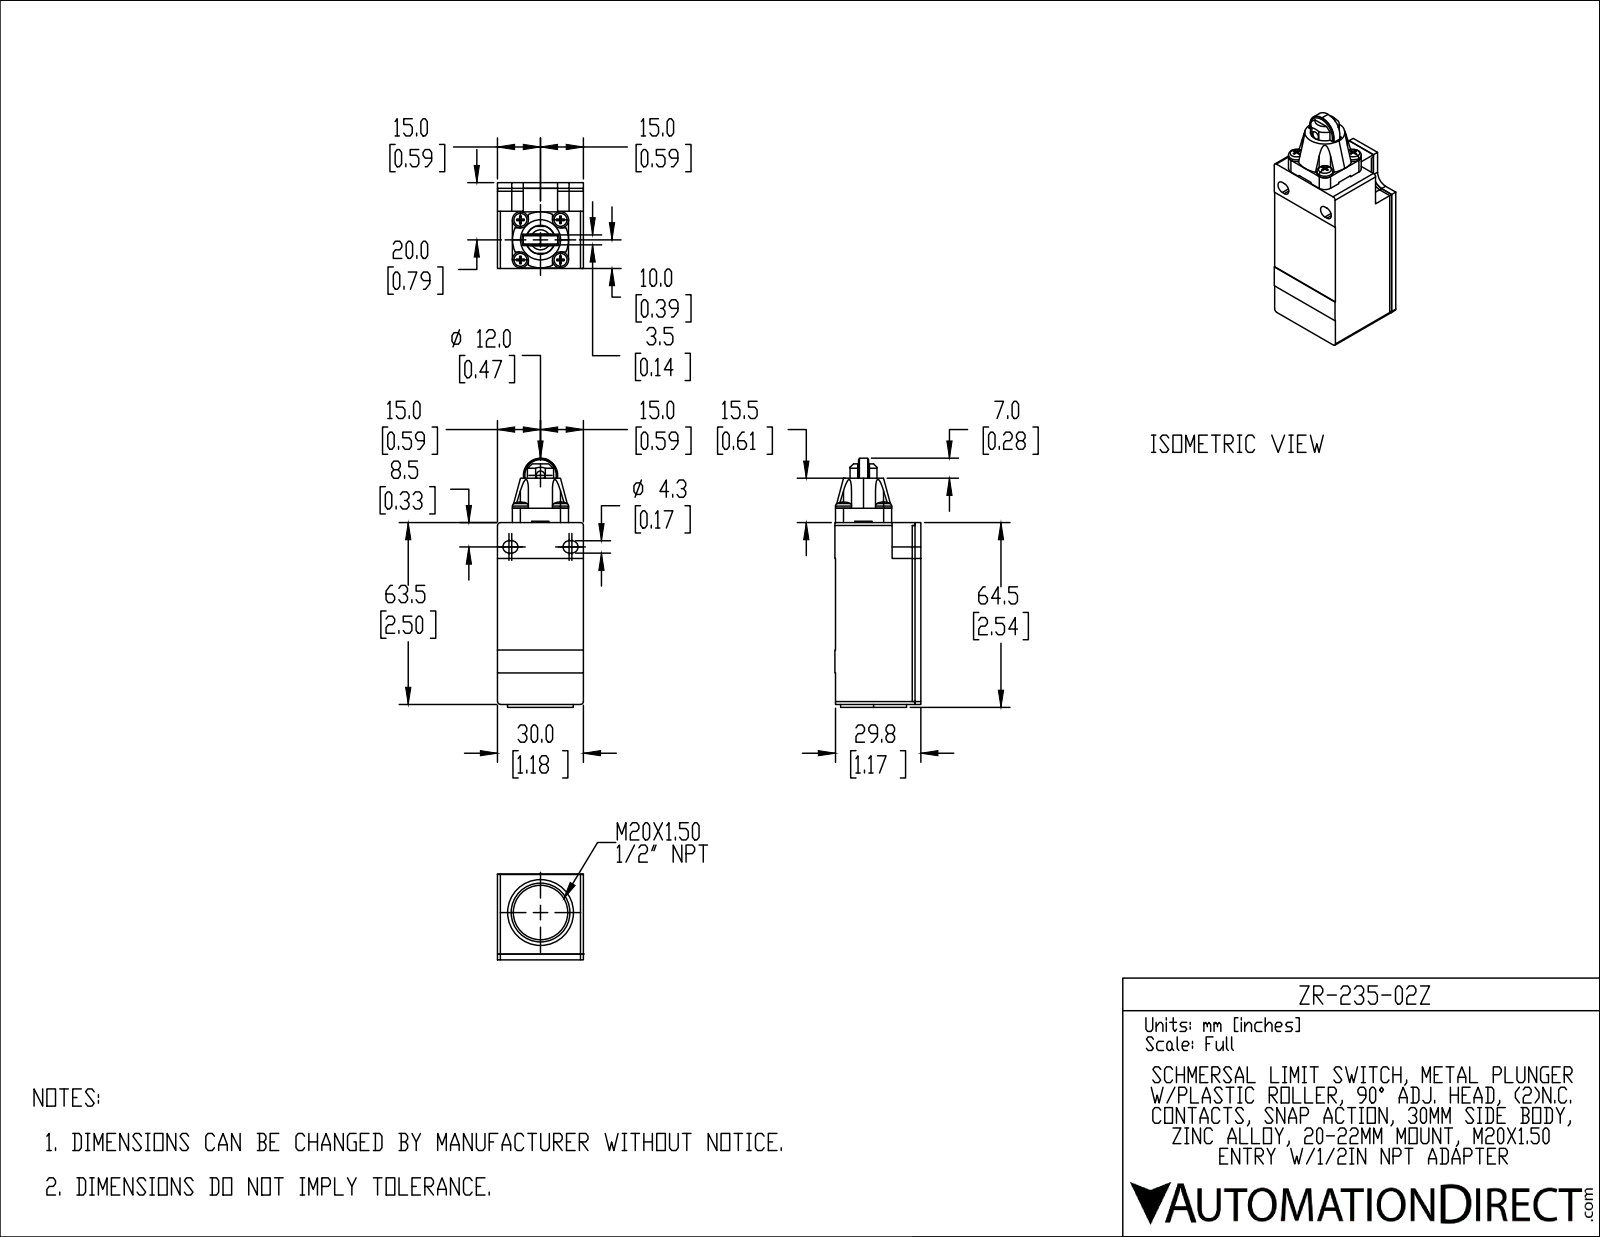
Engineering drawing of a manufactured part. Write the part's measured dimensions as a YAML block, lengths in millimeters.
part_name: "ZR-235-02Z"
step_written_by: "SolidWorks 2019 (AUTOMOTIVE_DESIGN)"
units: millimeters
bodies: {solids: 1, faces: 382, planar: 257, cylindrical: 99, other: 26}
overall_size: [87, 30, 30]
volume: 56080
surface_area: 13750
round_holes:
  - {diameter: 7, count: 3}
  - {diameter: 3, count: 1}
  - {diameter: 13, count: 1}
  - {diameter: 13.8, count: 1}
  - {diameter: 19, count: 1}
round_bosses_or_shafts:
  - {diameter: 5.4, count: 4}
  - {diameter: 6.5, count: 3}
  - {diameter: 5.6, count: 2}
  - {diameter: 23, count: 1}
  - {diameter: 12, count: 1}
  - {diameter: 10.5, count: 1}
  - {diameter: 7, count: 1}
partial_cylinders:
  - {radius: 0.5, count: 12}
  - {radius: 2.8, count: 8}
  - {radius: 1, count: 4}
  - {radius: 2.2, count: 4}
  - {radius: 2.8, count: 2}
  - {radius: 4, count: 2}
  - {radius: 4, count: 2}
  - {radius: 5, count: 1}
face_to_face_distances: [30, 29.8, 63.5, 5.3, 58.2, 3.8, 19.8, 9, 20, 10]
hole_center_spacings: [56.6, 76.8, 3.5, 20.5, 22]
